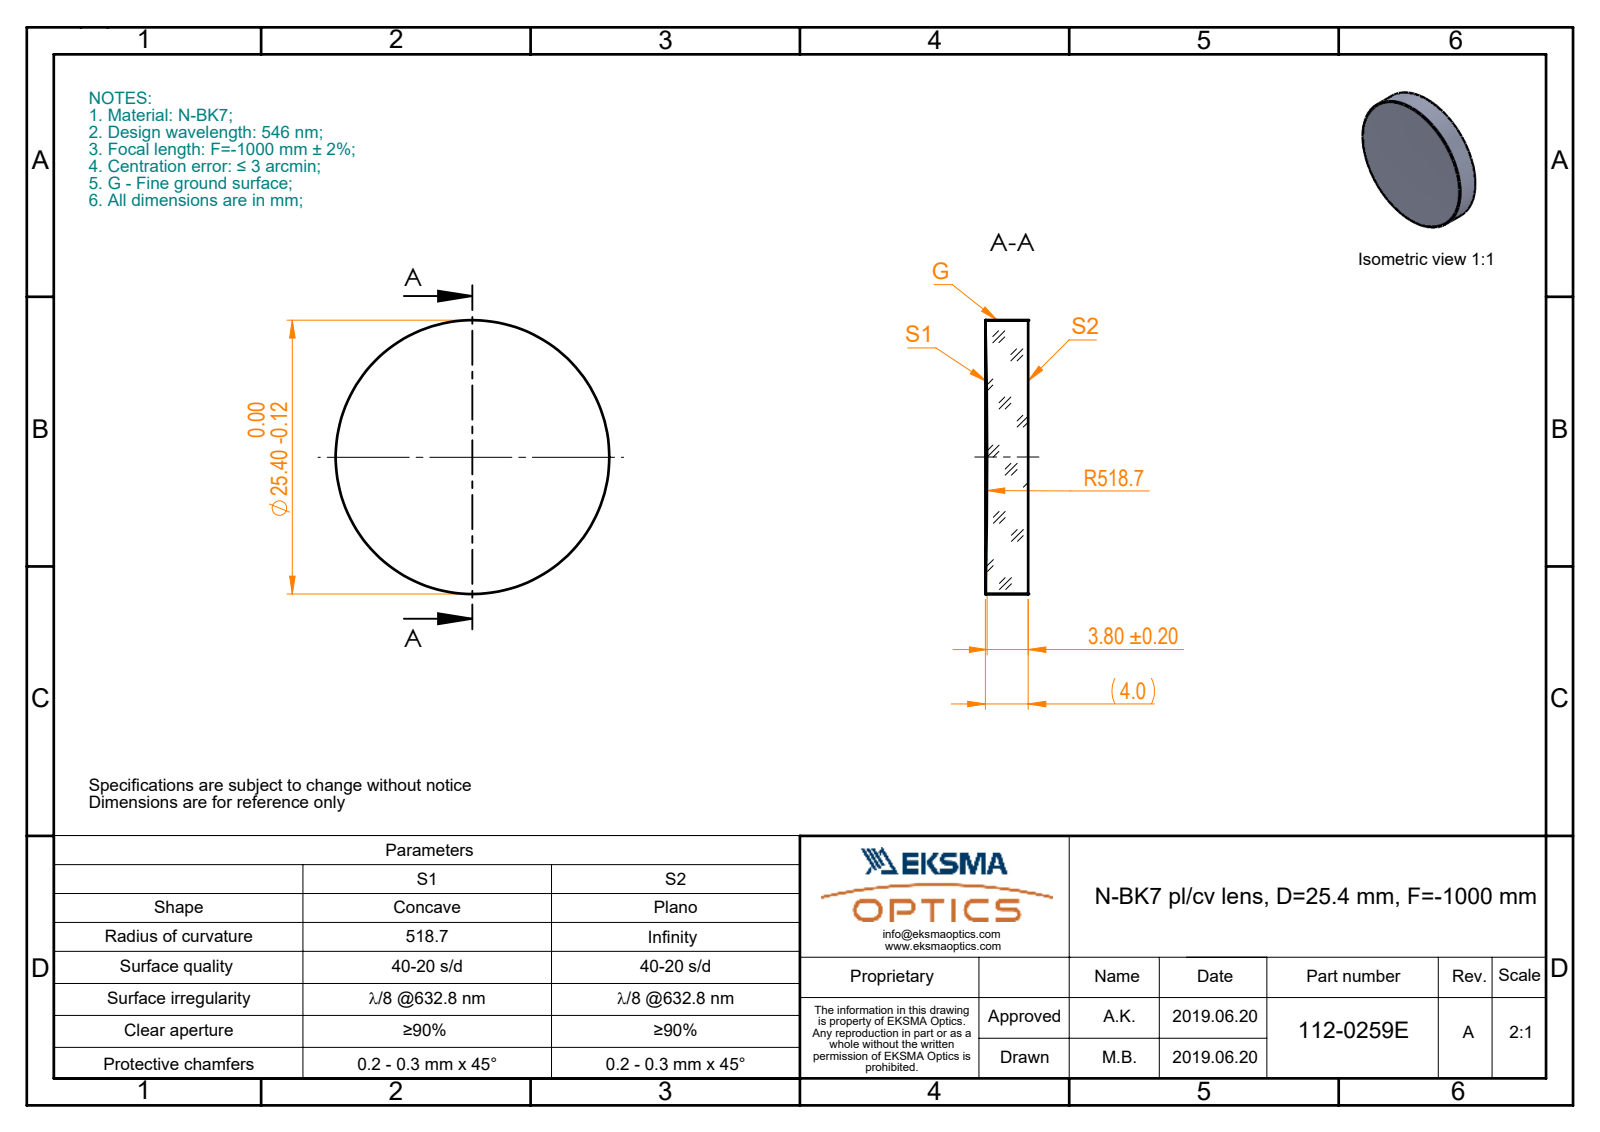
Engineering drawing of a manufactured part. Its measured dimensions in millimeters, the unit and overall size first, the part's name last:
Units: millimetres
Overall size (bounding box): 25.4 × 25.4 × 3.96
Round bosses / shafts (diameter × count): ⌀25.4 ×1
Volume: 1 965 mm³ · Surface area: 1 329 mm²
Bodies: 1 solid, 5 faces (1 planar, 2 cylindrical, 2 other)
Part name (STEP PRODUCT): 112-0259E BK7 pl-cv 25.4 F-1000
STEP written by: SolidWorks 2017 (CONFIG_CONTROL_DESIGN)
